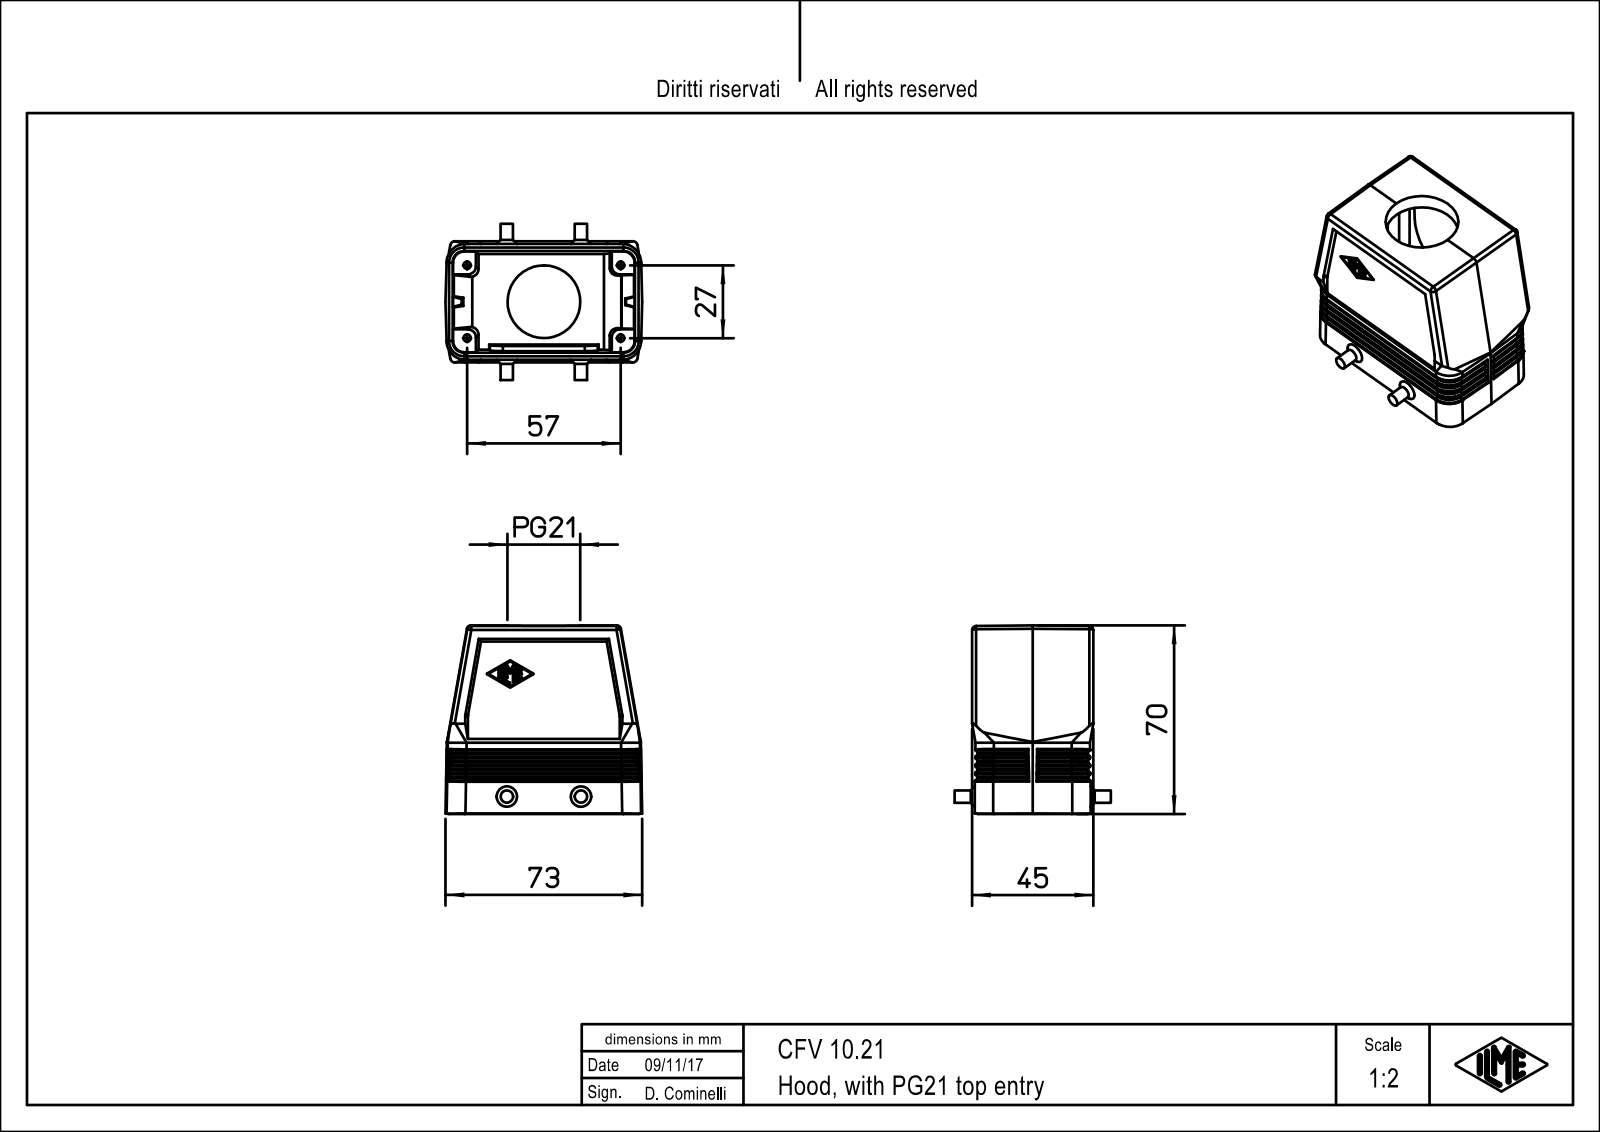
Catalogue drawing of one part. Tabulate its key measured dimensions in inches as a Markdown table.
| quantity | value |
| --- | --- |
| part name | CFV_10.21 |
| STEP written by | PTC Creo Elements/Direct Modeling 19.0E 27-Jun-2016 (C) Parametric Technology GmbH (AUTOMOTIVE_DESIGN) |
| units | inches |
| bodies | 1 solid, 351 faces (138 planar, 71 cylindrical, 142 other) |
| overall size | 2.874 × 2.756 × 2.283 |
| volume | 4.115 in³ |
| surface area | 51.49 in² |
| round holes (diameter × count) | 0.108 × 4, 1.063 × 1 |
| round bosses / shafts (diameter × count) | 0.181 × 2 |
| partial cylindrical surfaces (radius × count) | 0.02 × 17, 0.059 × 10, 0.276 × 8, 0.118 × 4, 0.165 × 4, 0.236 × 4, 0.787 × 1 |
| main face-to-face distances | 1.693, 0.335, 0.075, 0.079, 1.732, 0.039, 0.157, 1.772, 0.236, 0.447 |
| hole center spacings | 1.242, 1.063, 2.244, 2.483 |
